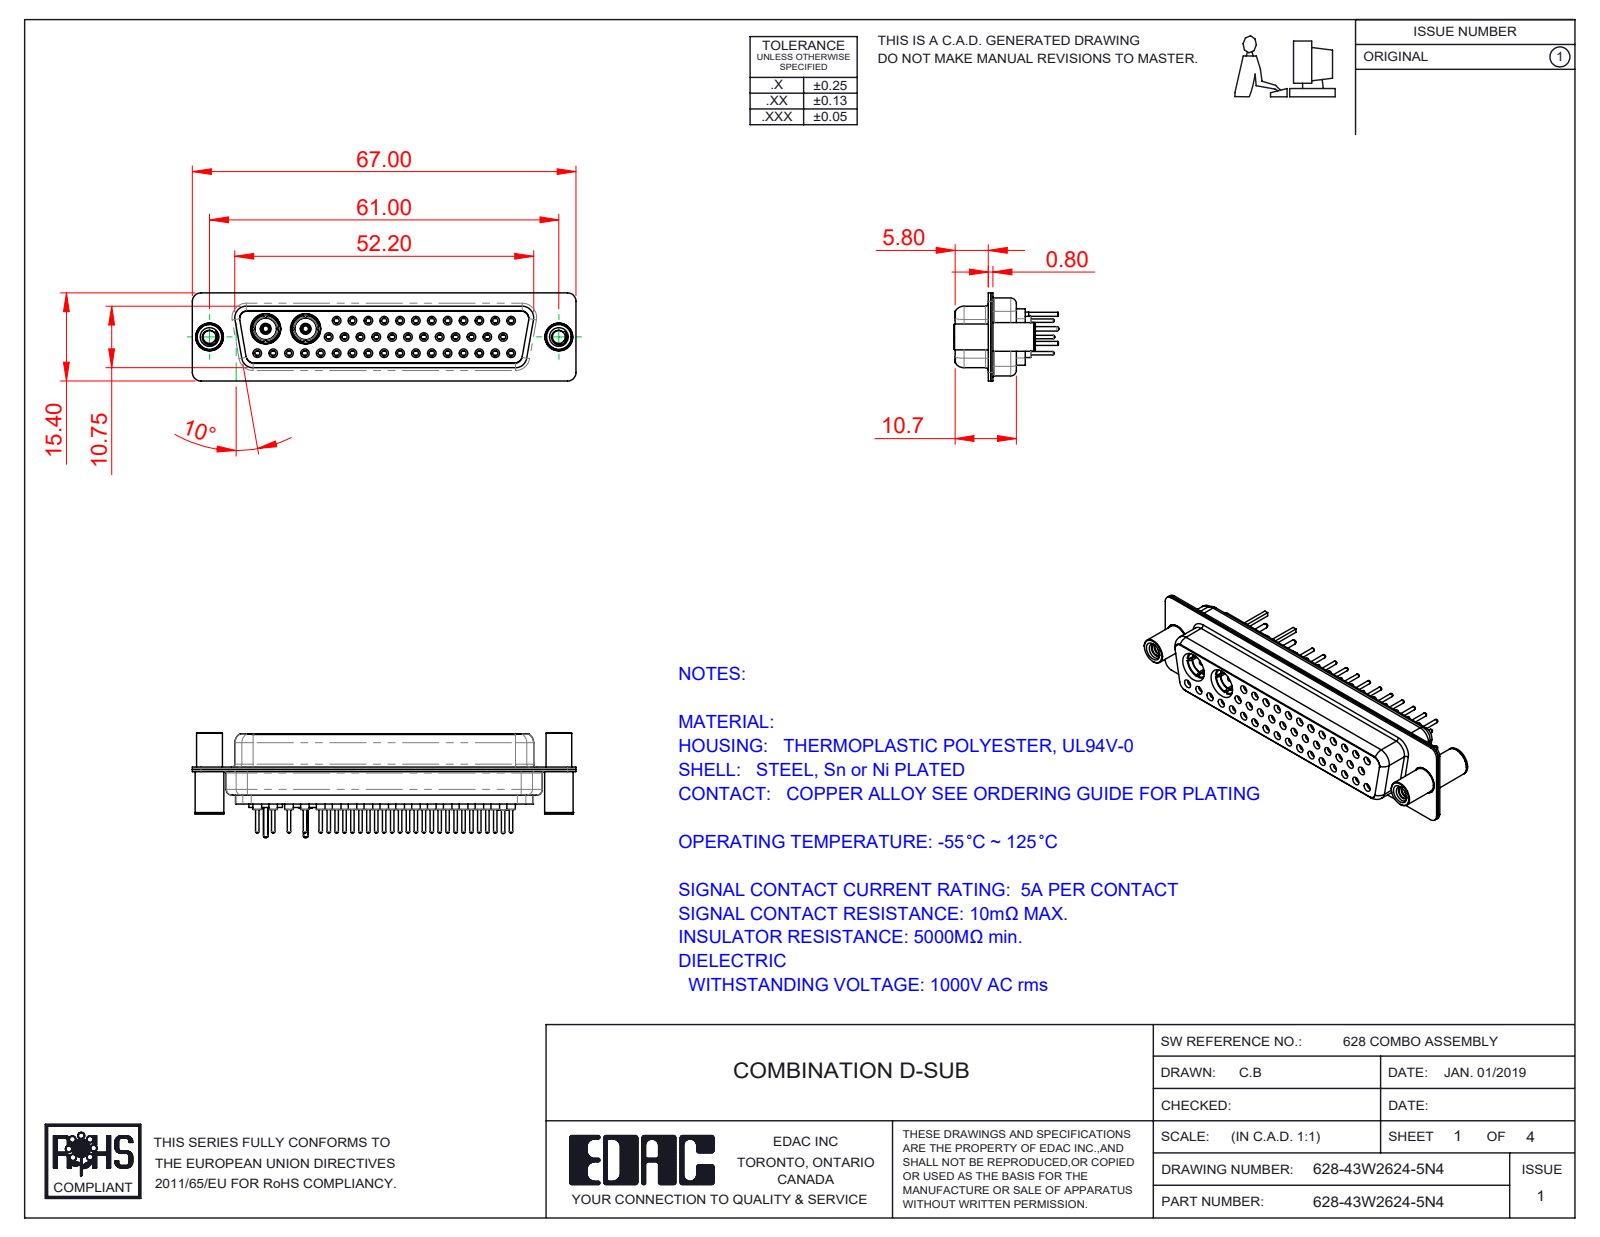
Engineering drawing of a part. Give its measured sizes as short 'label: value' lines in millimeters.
name: Insulator Pin_Straight PC Tail; 628Combo Contact Row 3_24; 628-43W2624-5N4; Co-Ax Plug_Straight PC Tail (+8 more)
written by: SolidWorks 2016 (CONFIG_CONTROL_DESIGN)
unit: mm
bodies: 54 solids, 2874 faces (802 planar, 1058 cylindrical, 1014 other)
size: 67 × 18.35 × 15.4
volume: 7 217 mm³; area: 15 510 mm²
holes: 43× ⌀1.1, 43× ⌀1.5, 41× ⌀0.9, 41× ⌀2, 29× ⌀1.6, 12× ⌀1.7, 4× ⌀4.85, 2× ⌀2.26, 2× ⌀2.83, 2× ⌀3.26, 2× ⌀3.3, 2× ⌀3.92
bosses: 41× ⌀2.2, 41× ⌀0.6, 12× ⌀1.6, 4× ⌀5, 2× ⌀5.85, 2× ⌀5.2, 2× ⌀4.95, 2× ⌀4.8
rounds: 16× R1.5, 12× R1.35, 12× R2, 8× R1.6, 4× R0.25, 4× R0.5, 4× R0.6, 4× R0.65
face distances: 0.4, 6.05, 11.33, 6.45, 1.87, 10.35, 10.93, 12.25, 6.2, 5.8
hole spacings: 2.77, 3.16, 5.54, 8.31, 11.08, 13.85, 16.62, 19.39
